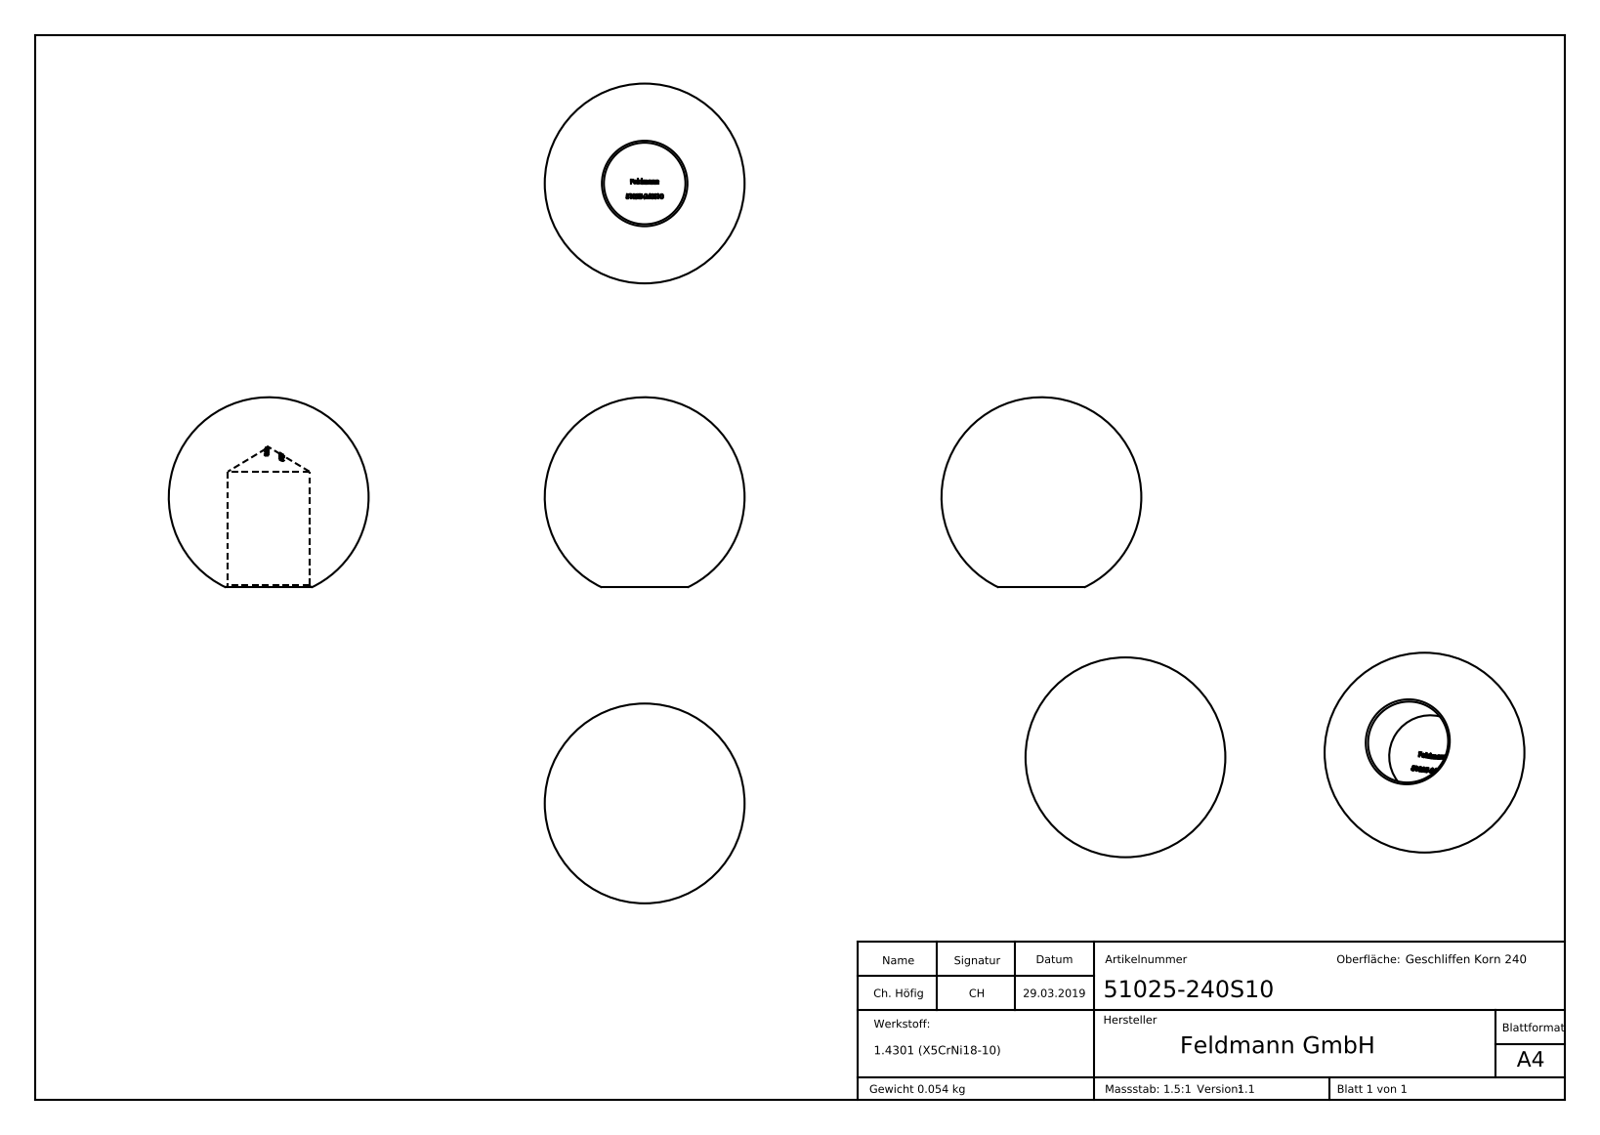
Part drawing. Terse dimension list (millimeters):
name: 51025-240S10
written by: SolidWorks 2015 (CONFIG_CONTROL_DESIGN)
unit: mm
bodies: 1 solid, 269 faces (109 planar, 2 cylindrical, 158 other)
size: 25 × 25 × 23.8
volume: 6 857 mm³; area: 2 438 mm²
holes: 1× ⌀10.2
face distances: 0.77, 1.35, 1.19, 1.88, 0.53, 0.84, 2.62, 3.46, 1.82, 0.35
